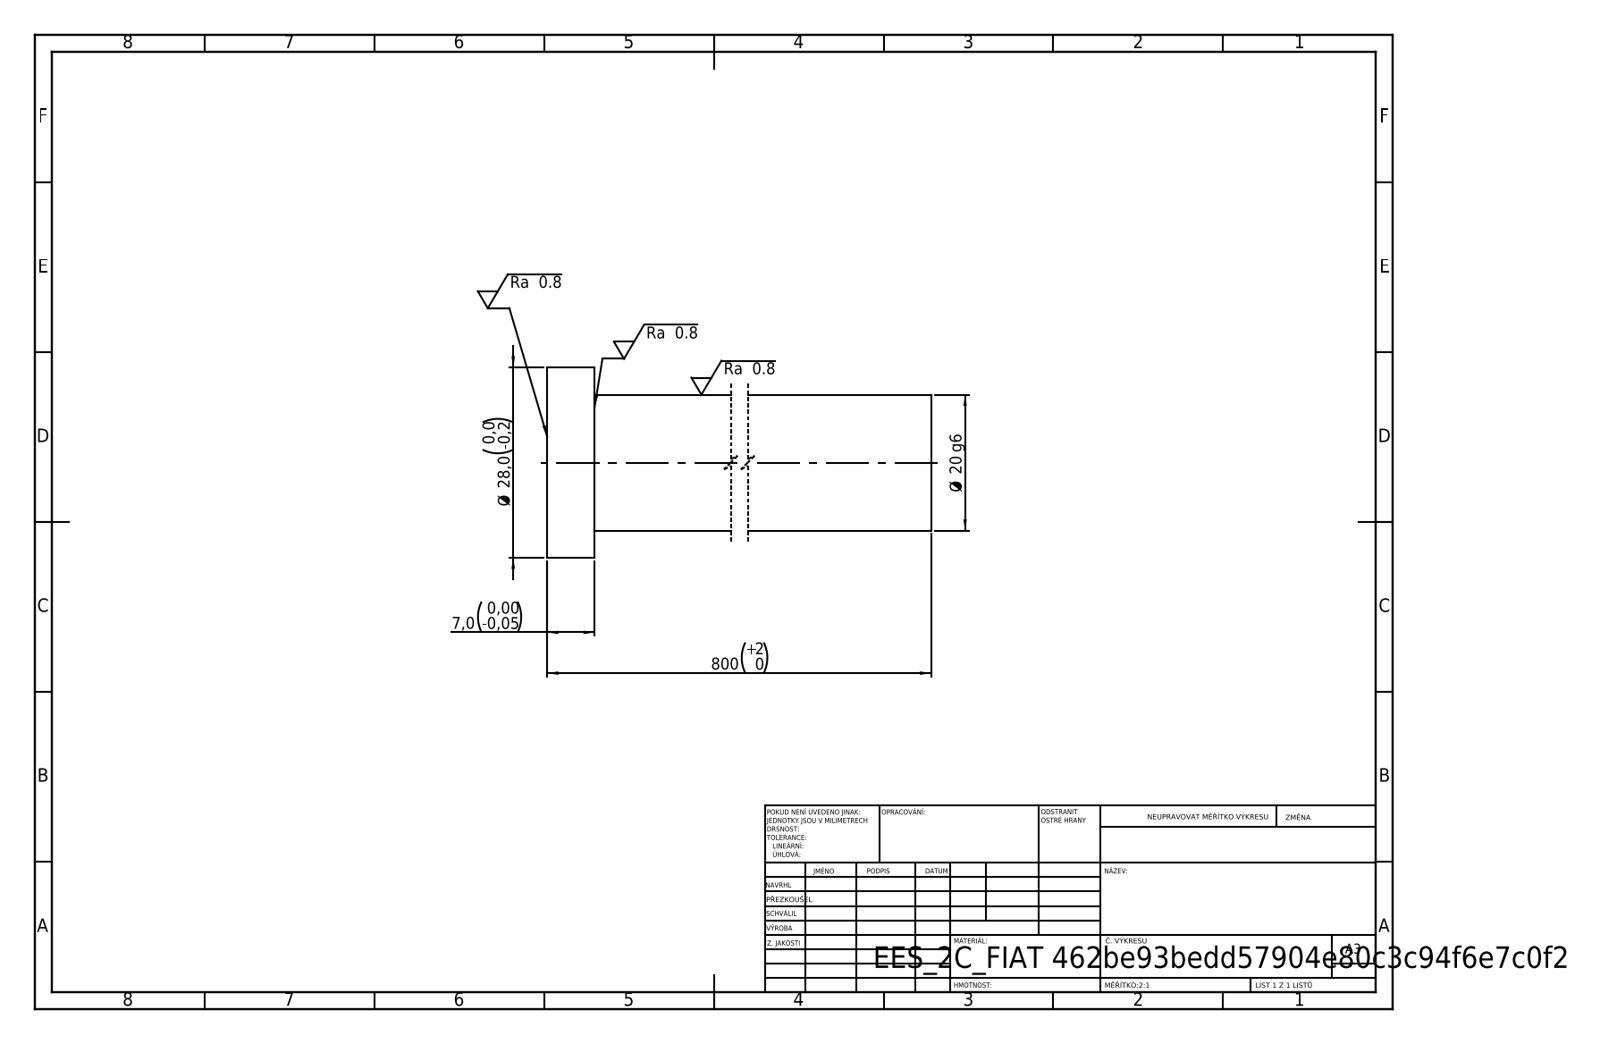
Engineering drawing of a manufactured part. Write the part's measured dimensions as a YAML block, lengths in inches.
step_written_by: "SolidWorks 2019 (CONFIG_CONTROL_DESIGN)"
units: inches
bodies: {solids: 1, faces: 7, planar: 3, cylindrical: 4, other: 0}
overall_size: [31.496, 1.102, 1.102]
volume: 15.47
surface_area: 80.09
round_bosses_or_shafts:
  - {diameter: 1.102, count: 1}
  - {diameter: 0.787, count: 1}
face_to_face_distances: [31.496, 0.276, 31.22]
